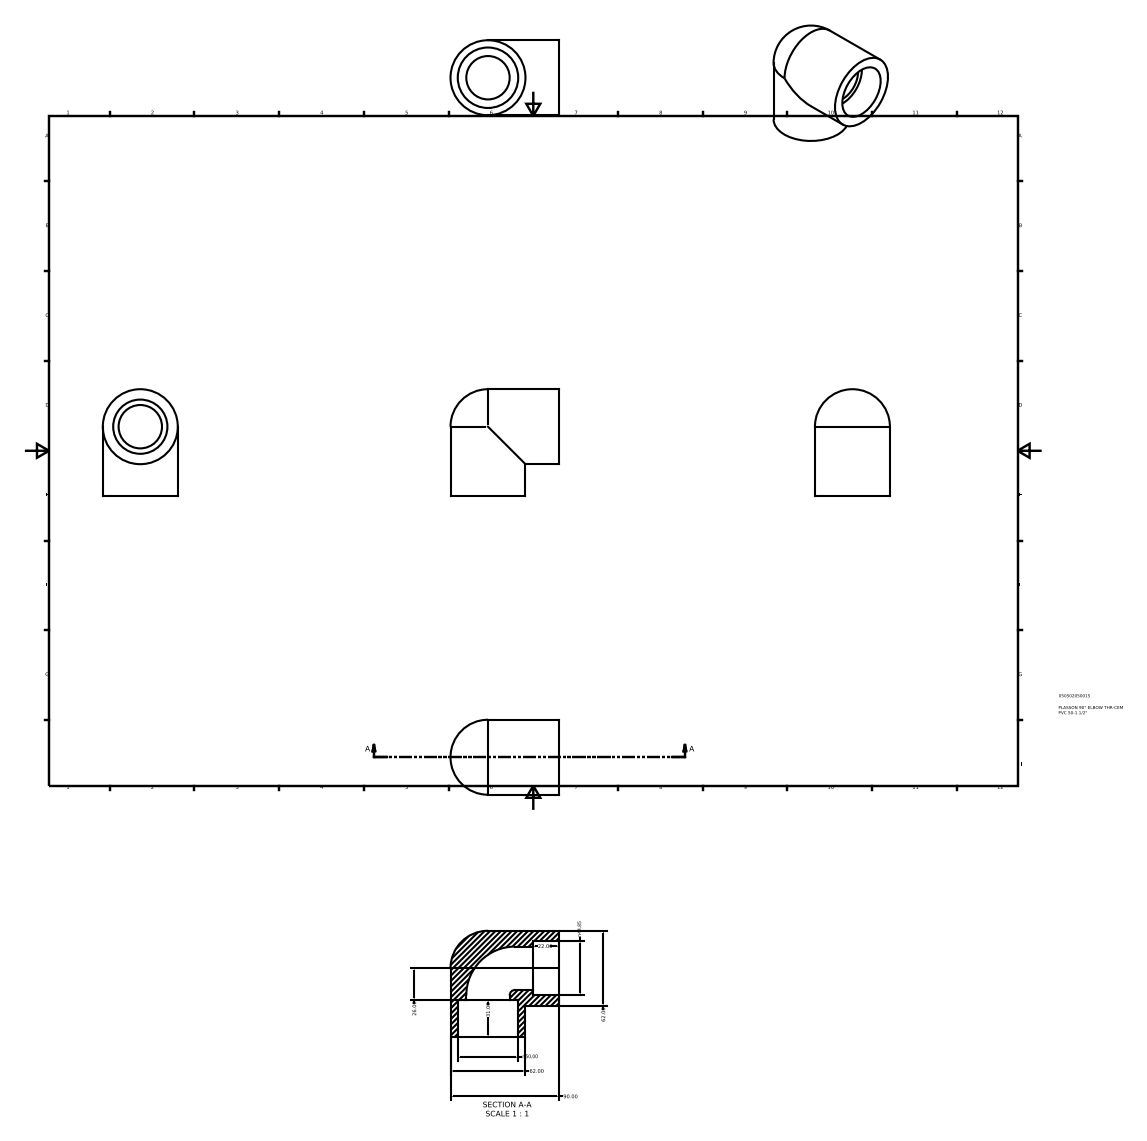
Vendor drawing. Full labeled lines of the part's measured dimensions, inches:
Part name (STEP PRODUCT): 050502050015
STEP written by: Autodesk Inventor 2015 (AUTOMOTIVE_DESIGN)
Units: inches
Bodies: 1 solid, 12 faces (4 planar, 6 cylindrical, 2 other)
Overall size (bounding box): 3.543 × 3.465 × 2.441
Volume: 11.72 in³ · Surface area: 61.65 in²
Round holes (diameter × count): ⌀1.413 ×2, ⌀1.765 ×1, ⌀1.969 ×1
Round bosses / shafts (diameter × count): ⌀2.441 ×2
Main face-to-face distances: 1.22, 0.866
